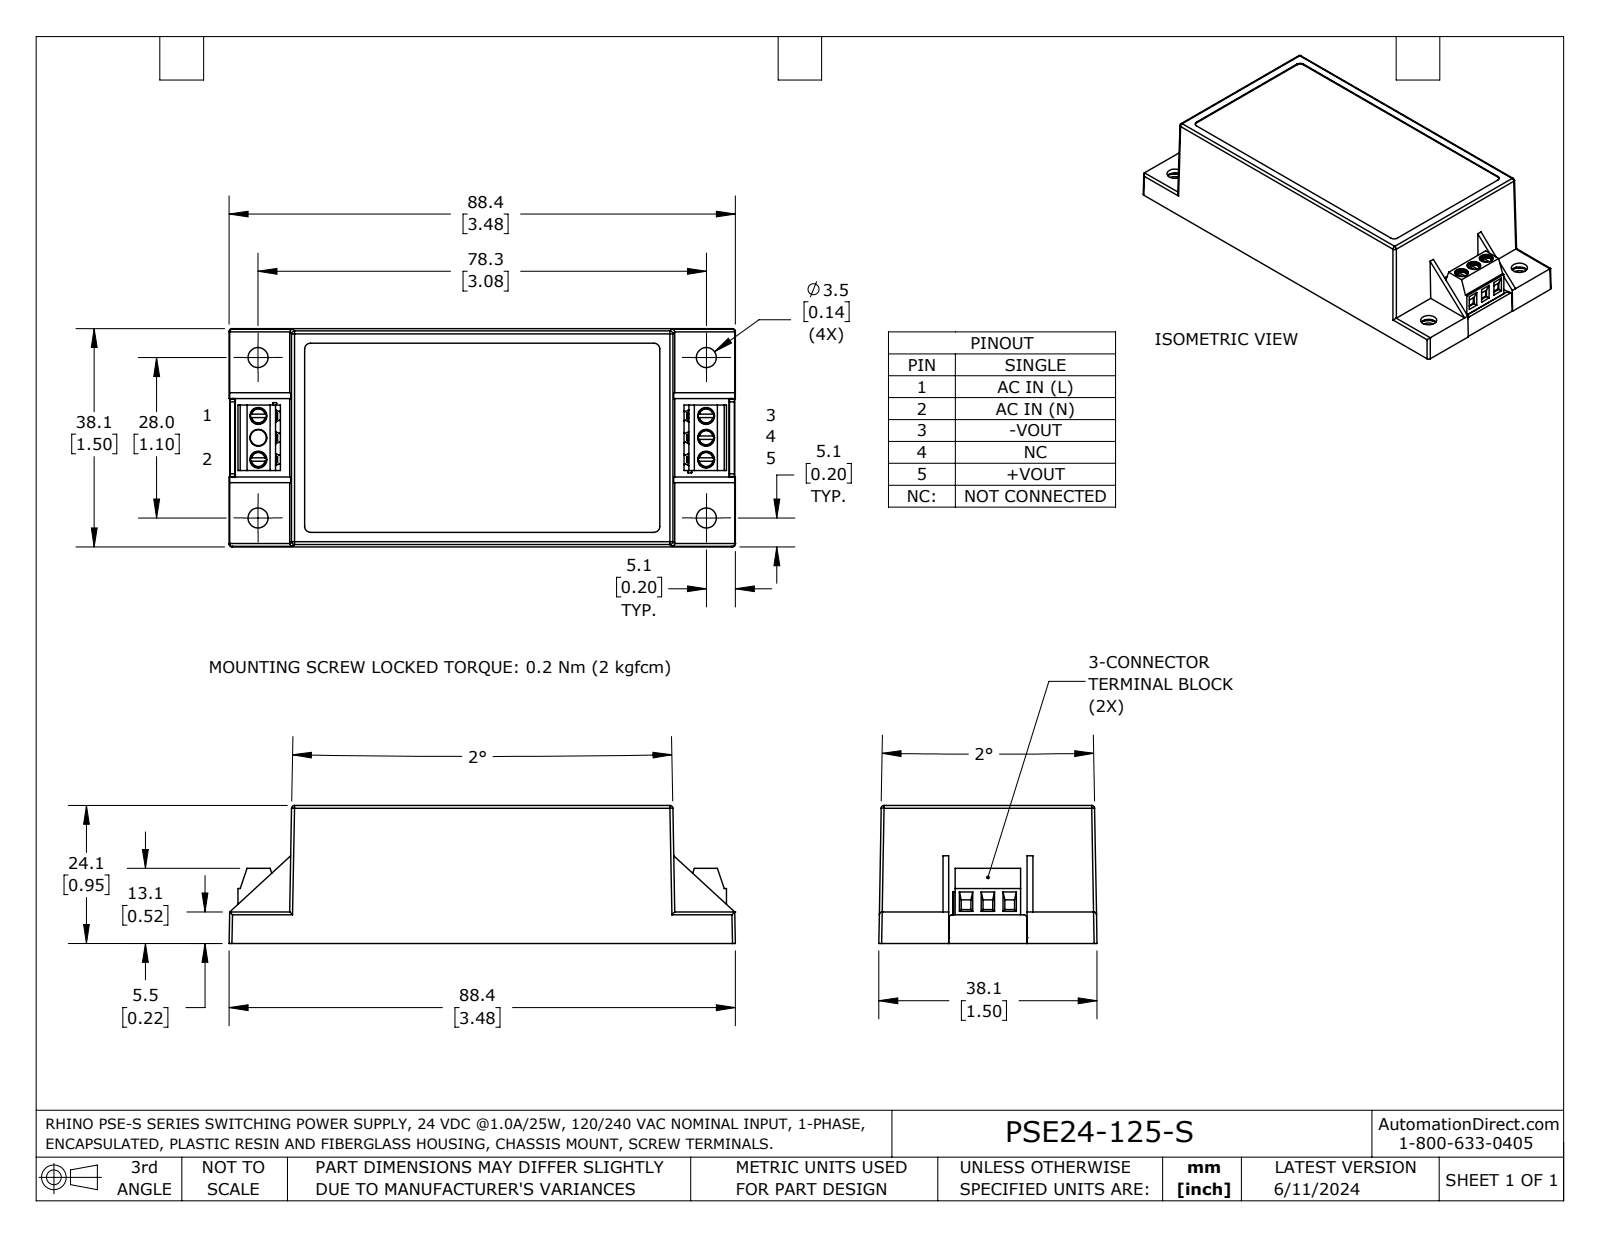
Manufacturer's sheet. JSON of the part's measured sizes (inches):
{"part_name": "PSE24-125-S", "step_written_by": "SolidWorks 2023 (AUTOMOTIVE_DESIGN)", "units": "inches", "bodies": {"solids": 4, "faces": 488, "planar": 328, "cylindrical": 126, "other": 34}, "overall_size": [3.48, 1.5, 0.983], "volume_in3": 0.709, "surface_area_in2": 38.52, "round_holes": [[0.116, 6], [0.138, 4], [0.11, 1]], "partial_cylinders_radius": [[0.02, 19], [0.009, 18], [0.006, 12], [0.004, 8], [0.008, 4], [0.01, 4], [0.039, 4], [0.079, 4]], "face_to_face_distances": [0.039, 0.902, 0.862, 0.941, 1.421, 2.575, 0.178, 0.724, 0.177, 0.725], "hole_center_spacings": [3.082, 0.15, 0.401, 0.551, 0.701, 3.107, 3.13, 3.159]}
